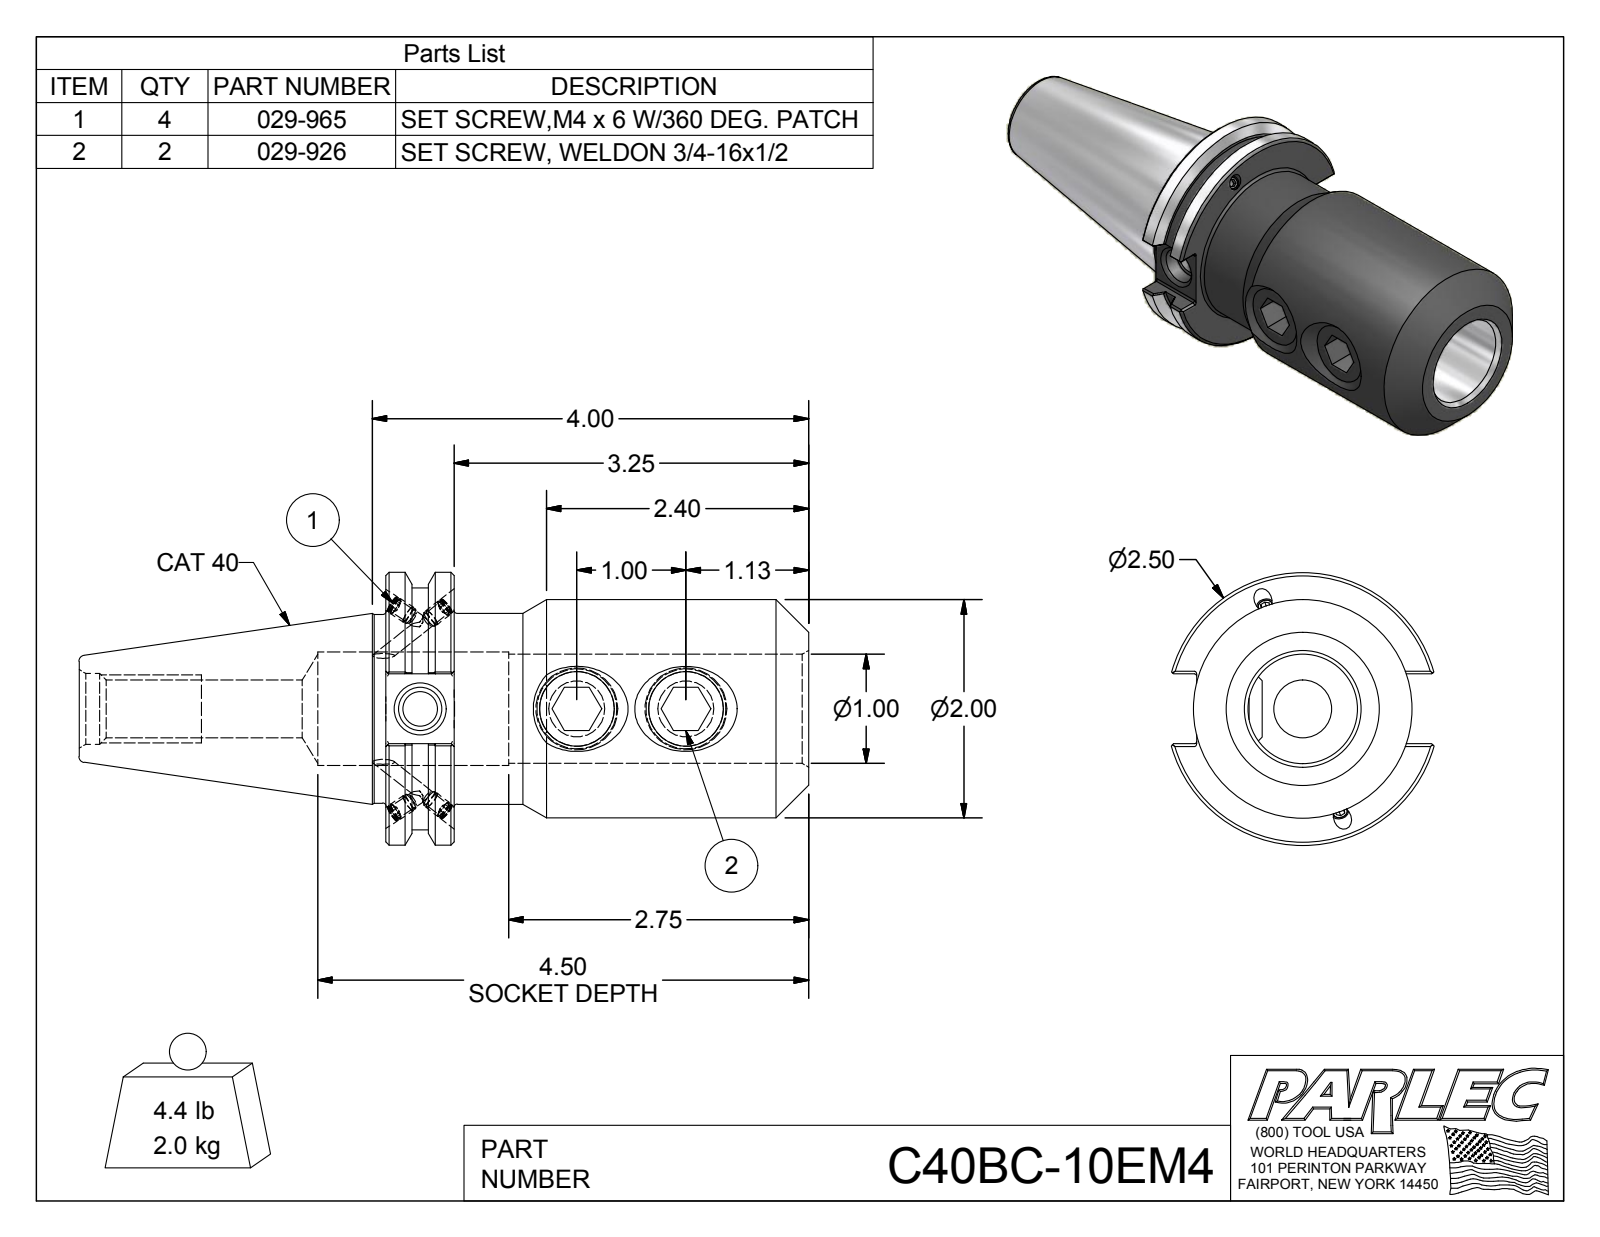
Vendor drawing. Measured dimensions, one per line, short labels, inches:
name: C40BC-10EM4; C40BC-10EM4-1; 029-926; 029-965
written by: Autodesk Inventor 2012 (AUTOMOTIVE_DESIGN)
unit: in
bodies: 7 solids, 197 faces (95 planar, 51 cylindrical, 51 other)
size: 6.687 × 2.5 × 2.406
volume: 11.99 in³; area: 70.02 in²
holes: 4× ⌀0.13, 4× ⌀0.161, 2× ⌀0.682, 1× ⌀0.315, 1× ⌀0.399, 1× ⌀0.527, 1× ⌀0.648, 1× ⌀1, 1× ⌀1.04
bosses: 4× ⌀0.165, 4× ⌀0.157, 2× ⌀0.75, 1× ⌀2.5, 1× ⌀2.219, 1× ⌀2, 1× ⌀1.75, 1× ⌀1.73
rounds: 12× R0.02
face distances: 0.625, 0.394, 3.875, 3.25, 0.472, 0.5, 0.866, 0.123, 0.517, 1.26
hole spacings: 1, 1.435, 2.435
